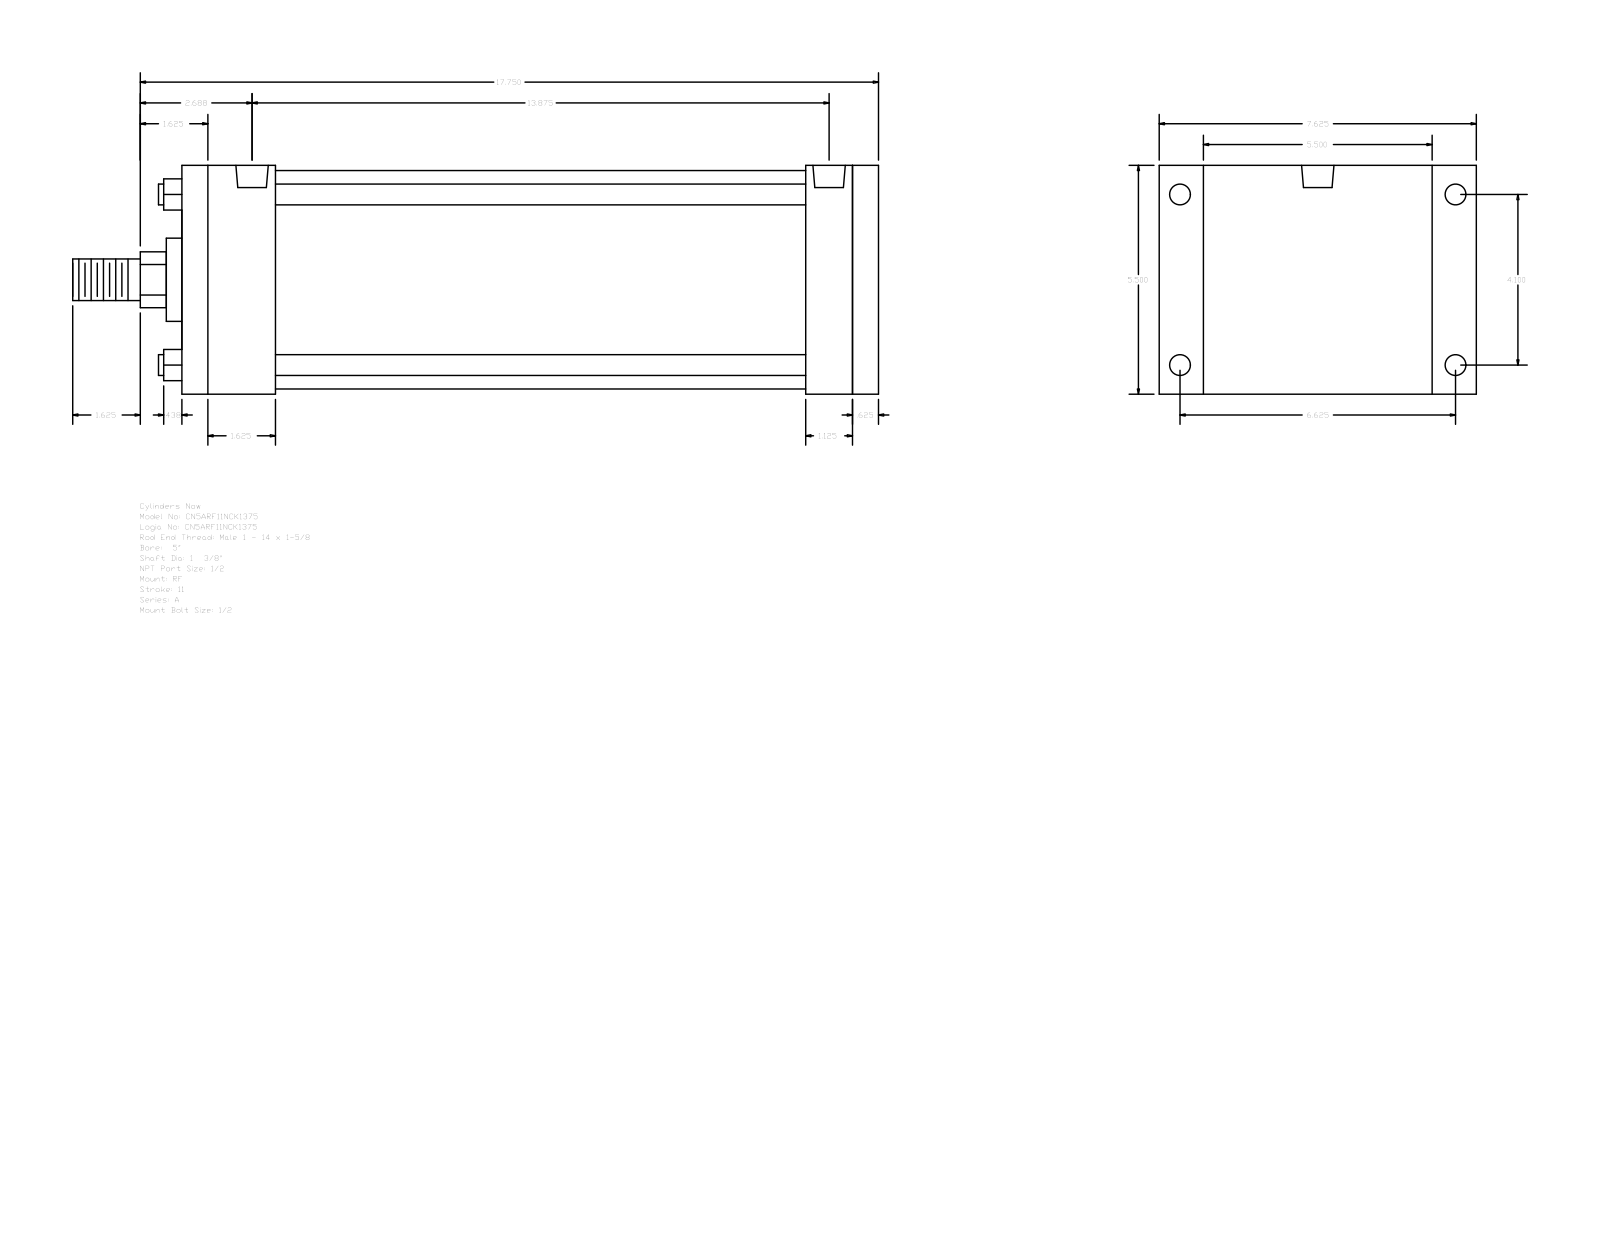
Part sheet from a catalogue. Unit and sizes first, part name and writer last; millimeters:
Units: millimetres
Overall size (bounding box): 492.12 × 193.68 × 139.7
Round holes (diameter × count): ⌀8.73 ×4, ⌀12.7 ×4, ⌀19.77 ×2
Round bosses / shafts (diameter × count): ⌀12.7 ×4, ⌀133.35 ×1, ⌀50.8 ×1, ⌀34.92 ×1, ⌀25.4 ×1
Partial cylindrical surfaces — rounded edges, fillets, slot ends (radius × count): R17.06 ×1
Main face-to-face distances: 139.7, 425.45, 409.58, 15.87, 57.15, 28.58, 352.43, 368.3, 381, 323.85
Hole centre spacings: 2.39, 104.14, 168.28, 197.9, 347.65, 350.04, 352.43
Bodies: 0 solids, 92 faces (64 planar, 28 cylindrical, 0 other)
Part name (STEP PRODUCT): A_RF__0500_1.375
STEP written by: GSSL Pune (CONFIG_CONTROL_DESIGN)
